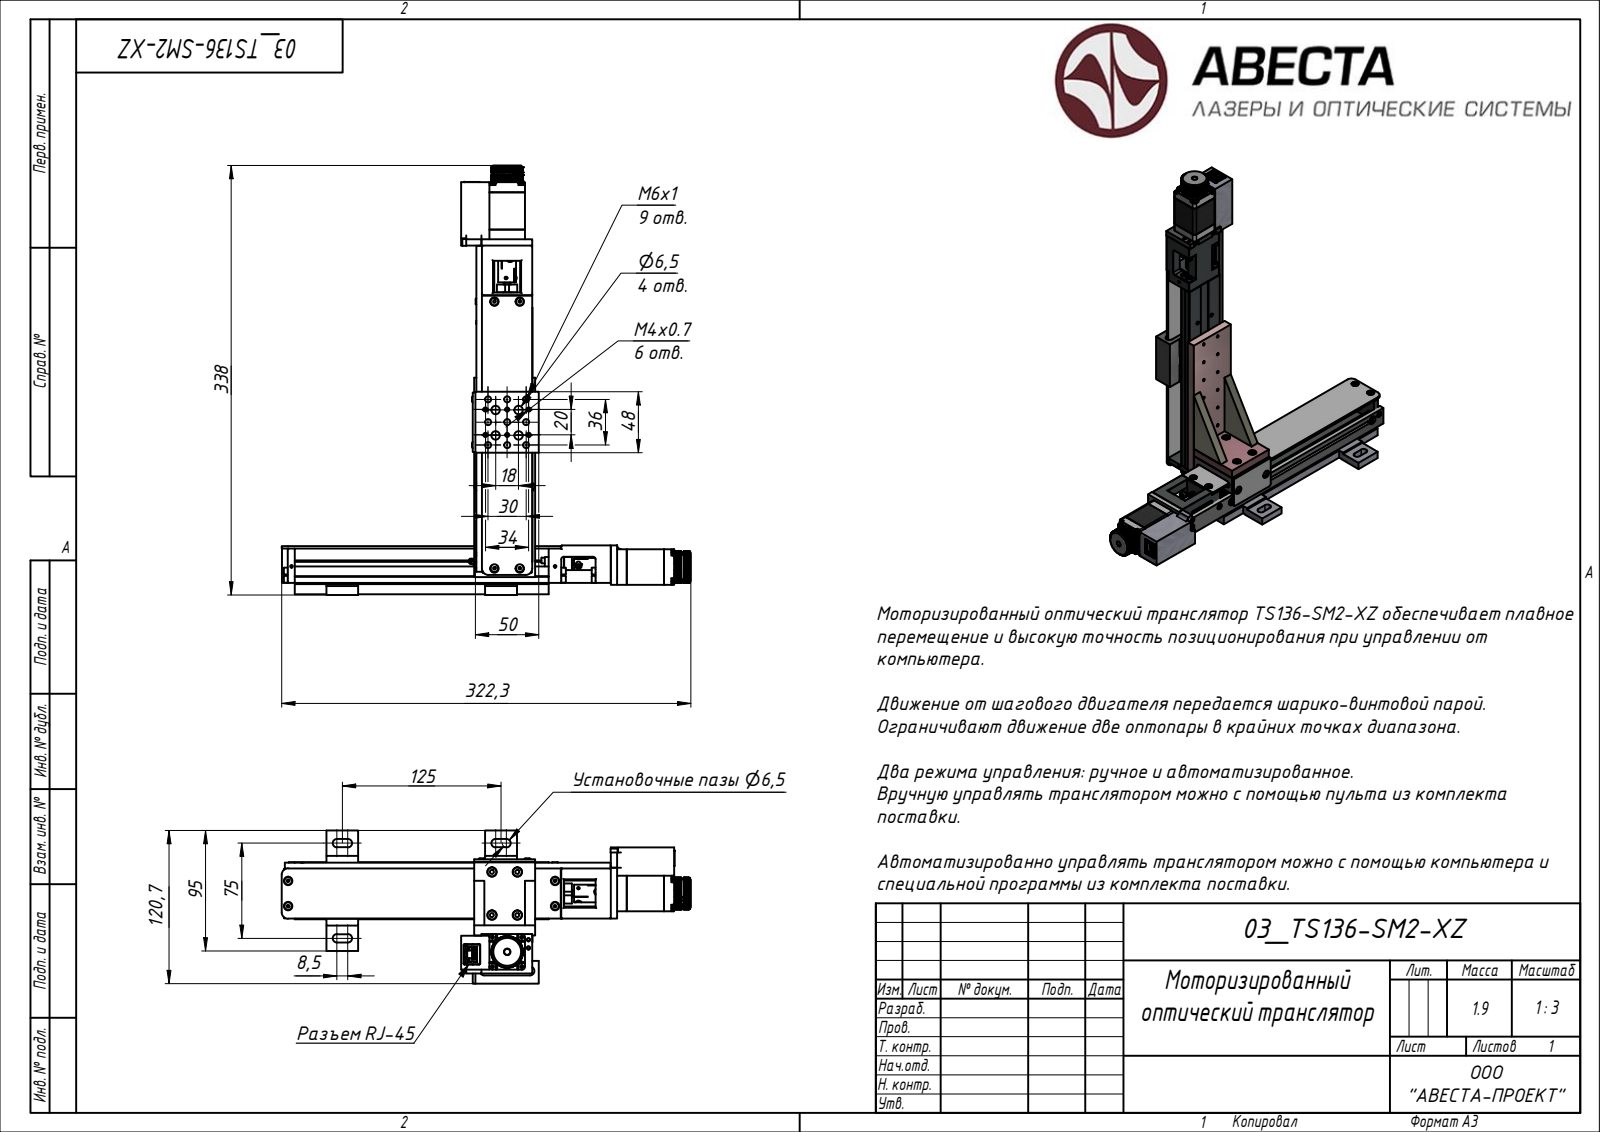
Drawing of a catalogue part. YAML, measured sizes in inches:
step_written_by: "Rhino 7.34 (AUTOMOTIVE_DESIGN)"
units: inches
bodies: {solids: 1, faces: 4562, planar: 2810, cylindrical: 1342, other: 410}
overall_size: [13.307, 12.689, 4.752]
volume: 40.42
surface_area: 424.6
round_holes:
  - {diameter: 0.256, count: 28}
  - {diameter: 0.134, count: 20}
  - {diameter: 0.097, count: 16}
  - {diameter: 0.128, count: 15}
  - {diameter: 0.295, count: 15}
  - {diameter: 0.098, count: 12}
  - {diameter: 0.041, count: 10}
  - {diameter: 0.194, count: 10}
  - {diameter: 0.087, count: 8}
  - {diameter: 0.15, count: 8}
  - {diameter: 0.194, count: 8}
  - {diameter: 0.197, count: 8}
round_bosses_or_shafts:
  - {diameter: 0.177, count: 20}
  - {diameter: 0.217, count: 12}
  - {diameter: 0.236, count: 8}
  - {diameter: 0.209, count: 8}
  - {diameter: 0.118, count: 8}
  - {diameter: 0.098, count: 8}
  - {diameter: 0.276, count: 6}
  - {diameter: 0.197, count: 6}
partial_cylinders:
  - {radius: 0.02, count: 72}
  - {radius: 0.118, count: 22}
  - {radius: 0.098, count: 20}
  - {radius: 0.079, count: 16}
  - {radius: 0.039, count: 8}
  - {radius: 0.128, count: 8}
  - {radius: 0.069, count: 4}
  - {radius: 0.094, count: 4}
face_to_face_distances: [0.079, 0.315, 0.02, 1.102, 1.161, 1.083, 0.197, 0.965, 1.496, 0.335]
hole_center_spacings: [0.787, 0.709, 0.922, 0.039, 0.669, 1.059, 1.575, 11.693]
